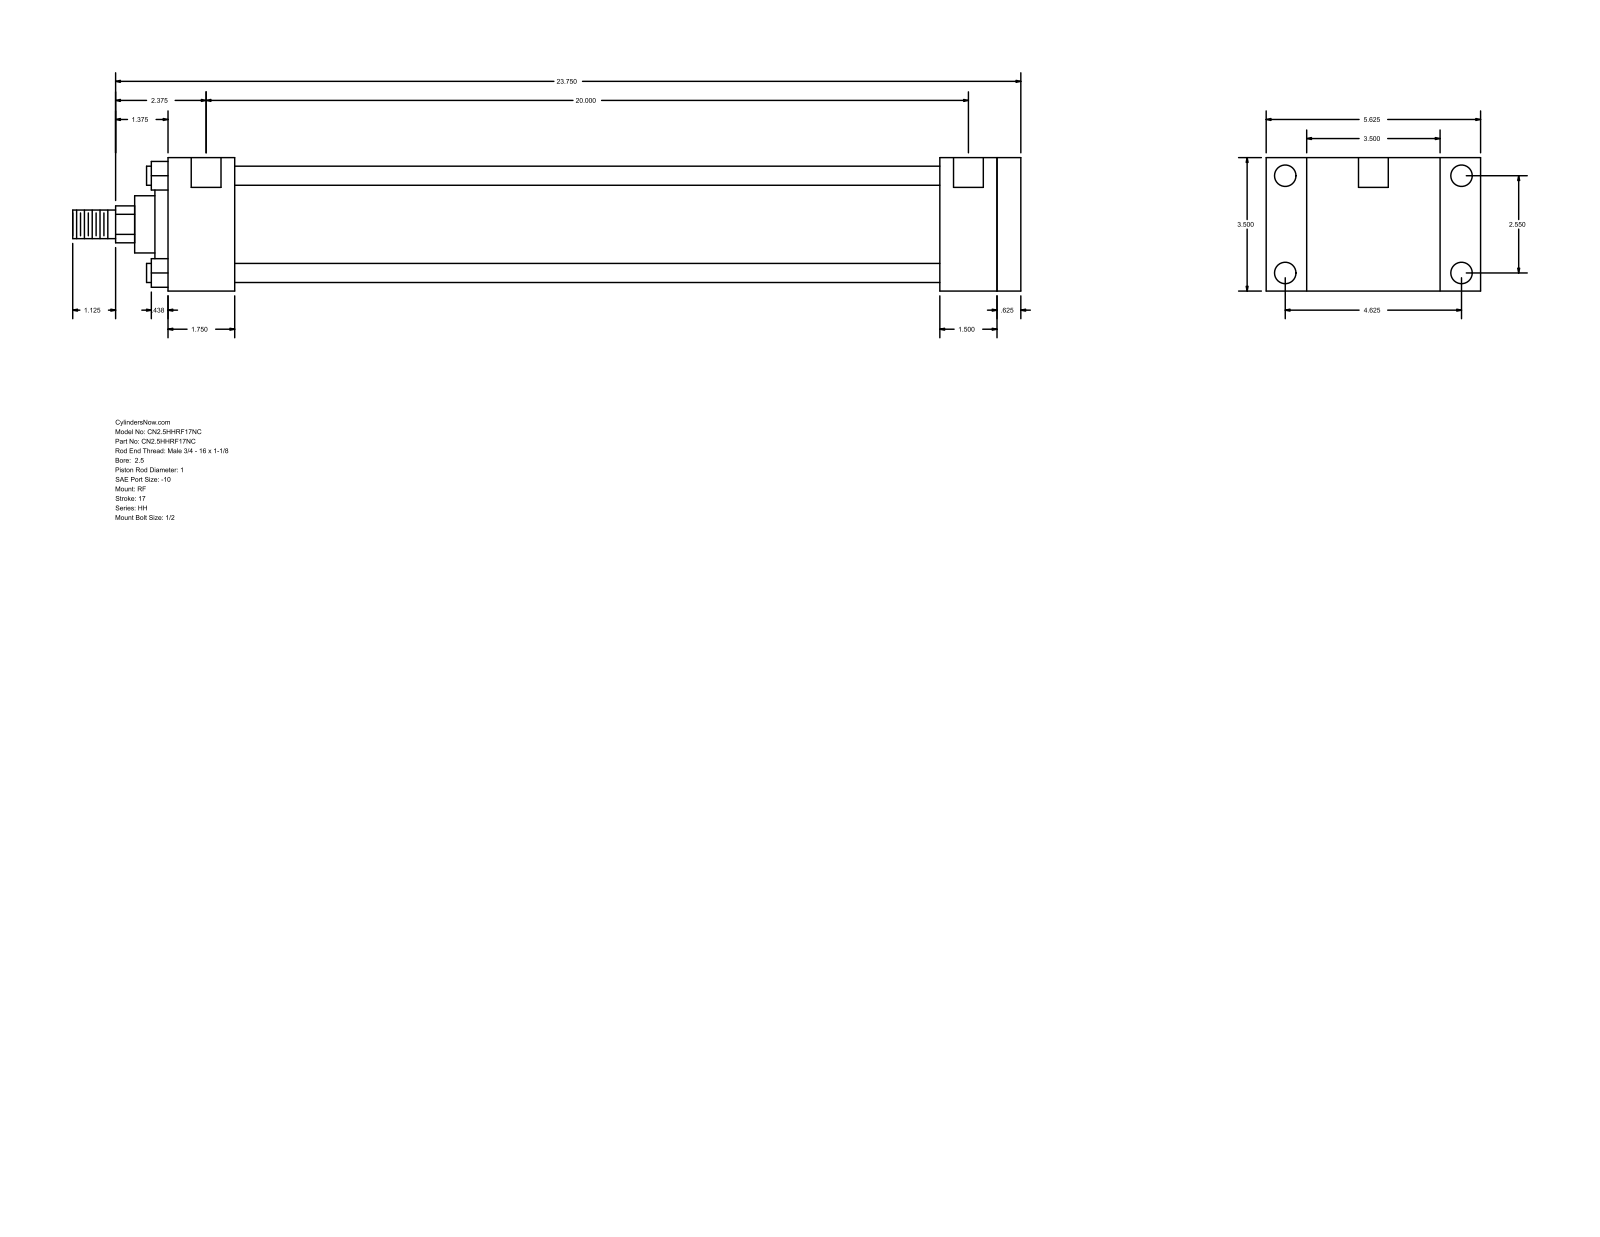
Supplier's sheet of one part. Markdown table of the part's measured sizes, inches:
| quantity | value |
| --- | --- |
| part name | HH_RF__0250_1 |
| STEP written by | GSSL Pune (CONFIG_CONTROL_DESIGN) |
| units | inches |
| bodies | 0 solids, 94 faces (65 planar, 29 cylindrical, 0 other) |
| overall size | 24.875 × 5.625 × 3.5 |
| round holes (diameter × count) | 0.219 × 4, 0.563 × 4, 0.781 × 2 |
| round bosses / shafts (diameter × count) | 0.5 × 4, 2.875 × 1, 2.375 × 1, 1.5 × 1, 1 × 1, 0.75 × 1 |
| partial cylindrical surfaces (radius × count) | 0.484 × 1 |
| main face-to-face distances | 3.5, 0.625, 21.75, 22.375, 1.75, 20, 20.625, 20.25, 18.5, 1.5 |
| hole center spacings | 2.55, 4.625, 5.281, 20.125, 0.062, 0.063, 20, 20.062 |
